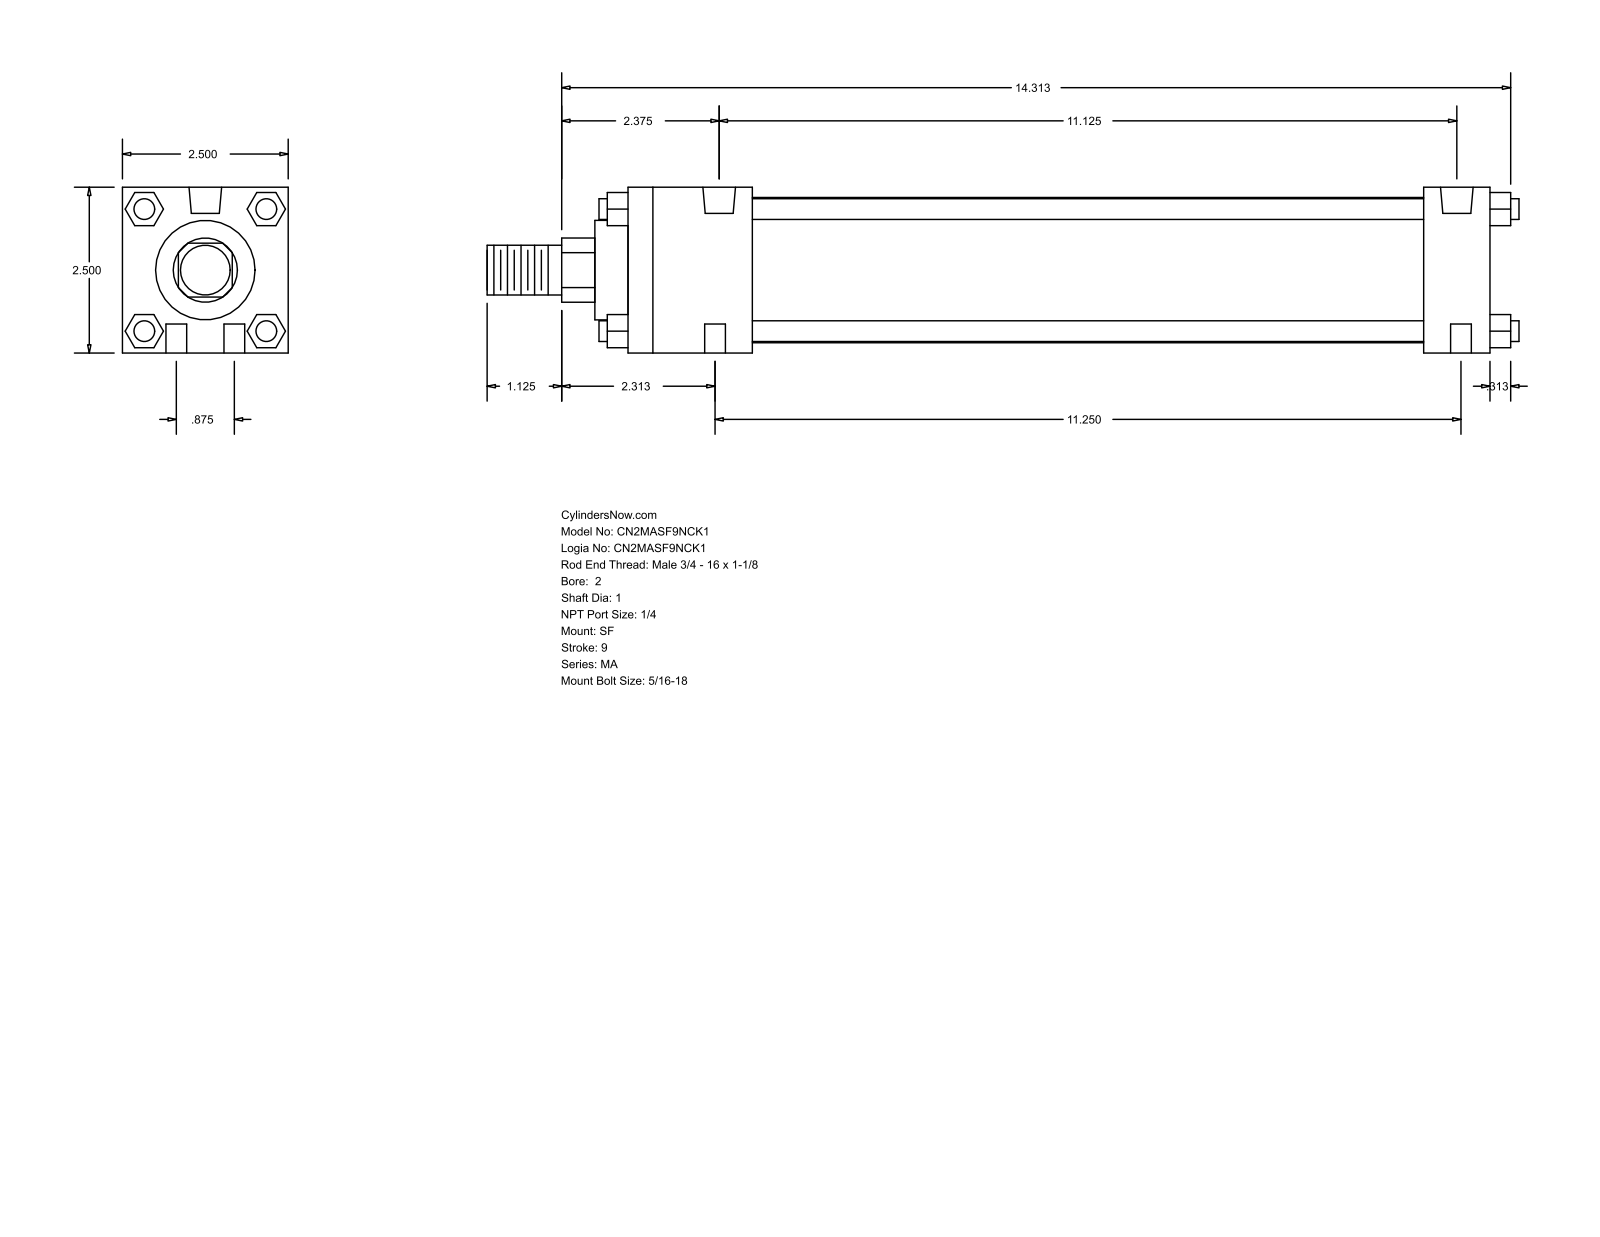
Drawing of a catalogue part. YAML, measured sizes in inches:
part_name: "MA_SF__0200_1"
step_written_by: "GSSL Pune (CONFIG_CONTROL_DESIGN)"
units: inches
bodies: {solids: 0, faces: 124, planar: 94, cylindrical: 30, other: 0}
overall_size: [15.563, 2.5, 2.5]
round_holes:
  - {diameter: 0.313, count: 6}
  - {diameter: 0.492, count: 2}
round_bosses_or_shafts:
  - {diameter: 0.313, count: 4}
  - {diameter: 2.19, count: 1}
  - {diameter: 1.5, count: 1}
  - {diameter: 1, count: 1}
  - {diameter: 0.75, count: 1}
partial_cylinders:
  - {radius: 0.484, count: 1}
face_to_face_distances: [2.5, 13, 0.5, 1, 12, 1.875, 10.125, 11.125, 0.92, 1.593]
hole_center_spacings: [0.442, 11.196, 0.875, 11.125, 11.25, 11.284]
